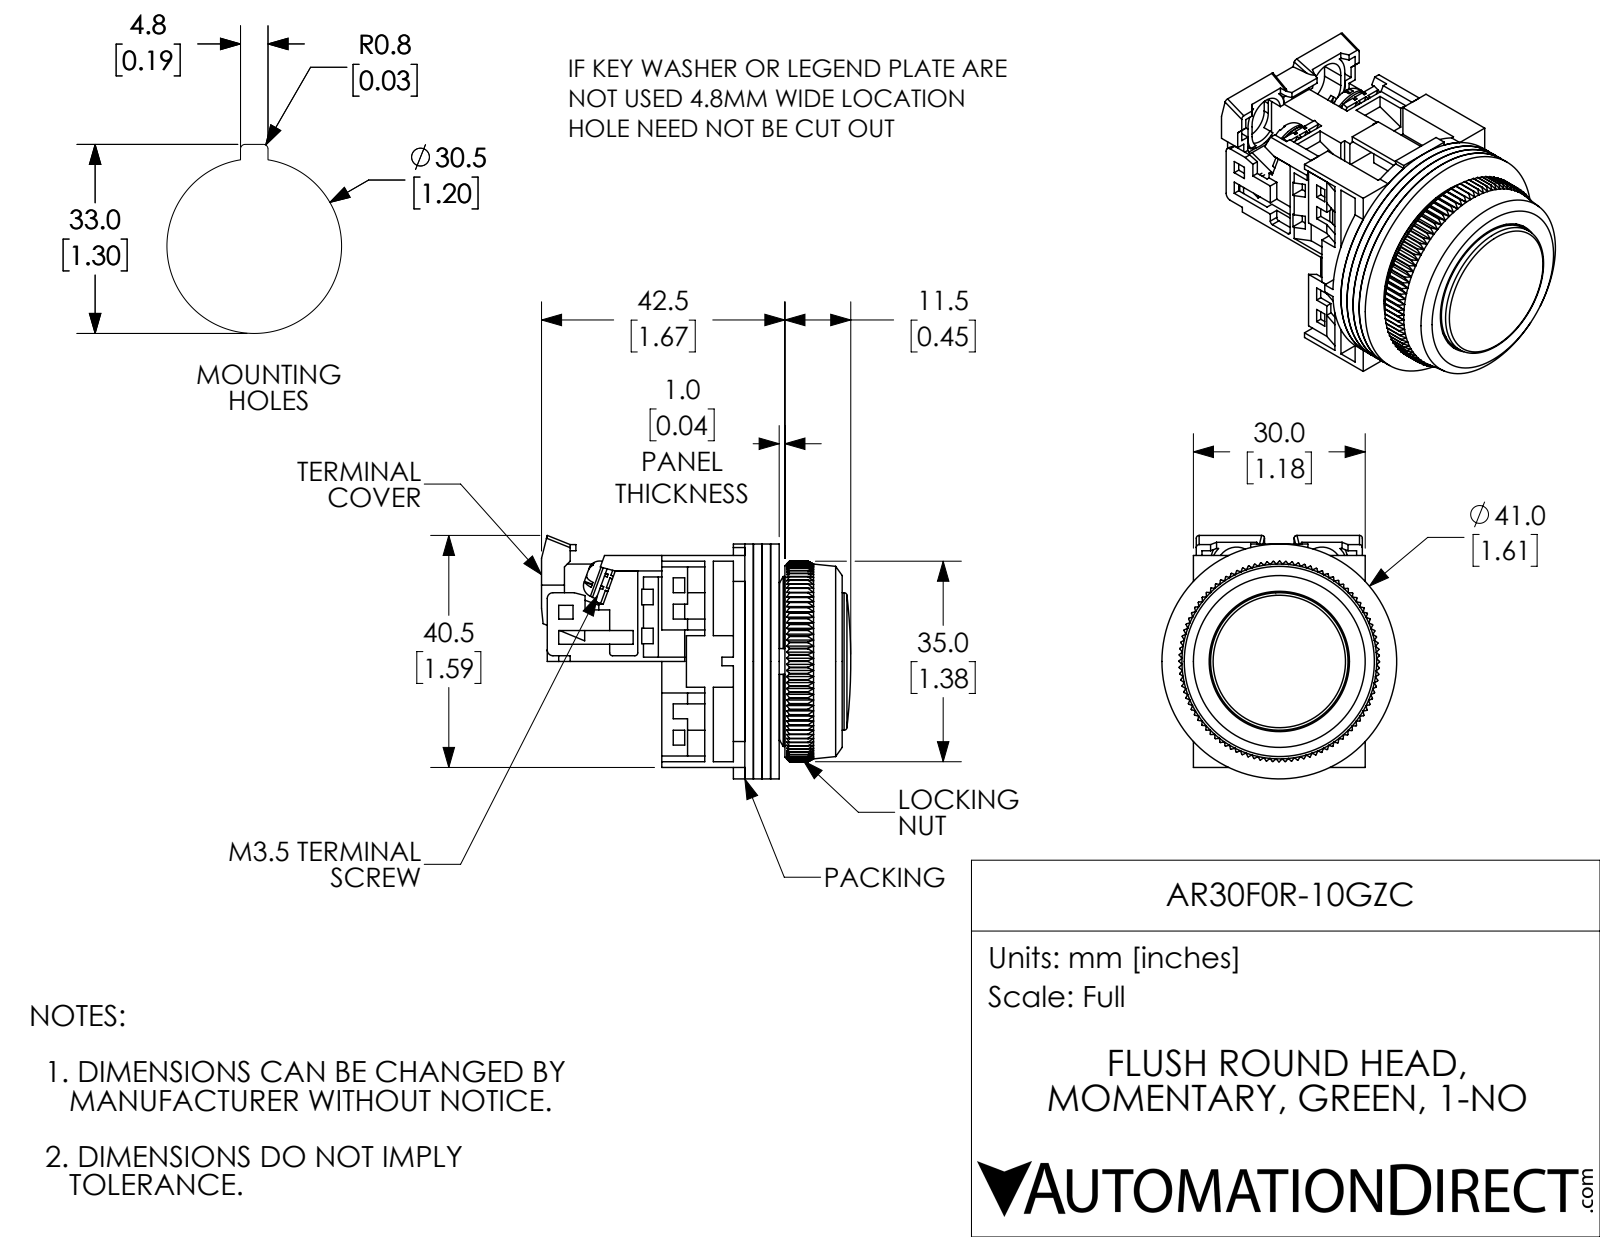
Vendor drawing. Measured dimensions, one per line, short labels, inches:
name: AR30F0R-10GZC
written by: SolidWorks 2017 (AUTOMOTIVE_DESIGN)
unit: in
bodies: 16 solids, 1258 faces (798 planar, 249 cylindrical, 211 other)
size: 2.125 × 1.673 × 1.614
volume: 1.595 in³; area: 47.89 in²
holes: 4× ⌀0.138, 2× ⌀0.142, 1× ⌀0.118, 1× ⌀0.472, 1× ⌀0.709, 1× ⌀0.787, 1× ⌀0.827, 1× ⌀0.945, 1× ⌀0.965, 1× ⌀1.122, 1× ⌀1.252
bosses: 2× ⌀0.26, 2× ⌀0.138, 1× ⌀1.614, 1× ⌀1.181, 1× ⌀0.906, 1× ⌀0.866, 1× ⌀0.551
rounds: 8× R0.059, 6× R0.02, 2× R0.039, 2× R0.138, 2× R0.177, 1× R0.118, 1× R0.398, 1× R0.449
face distances: 0.059, 0.118, 0.177, 0.039, 0.197, 0.079, 0.689, 1.417, 0.256, 0.138
hole spacings: 0.579, 0.61
